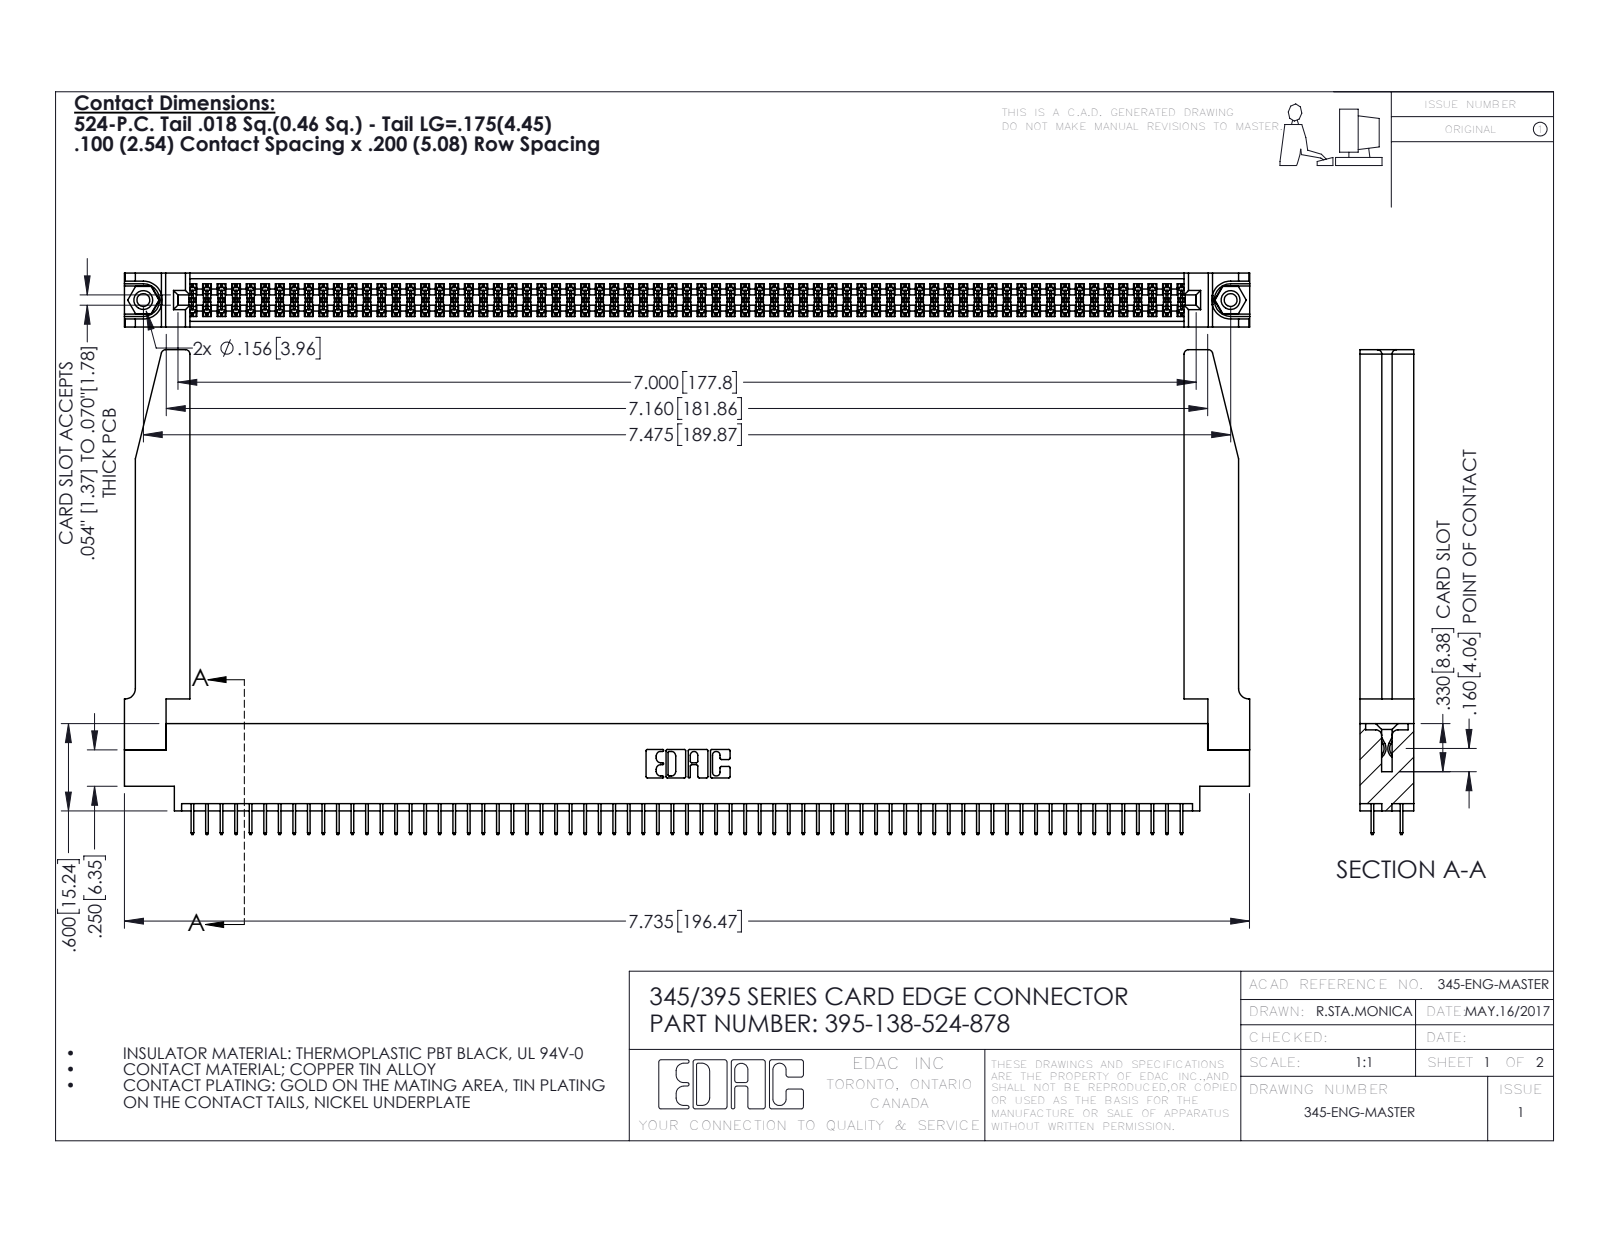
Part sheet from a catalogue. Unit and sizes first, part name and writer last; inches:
Units: inches
Overall size (bounding box): 7.736 × 3.332 × 0.37
Round holes (diameter × count): ⌀0.089 ×2, ⌀0.125 ×2, ⌀0.156 ×2, ⌀0.064 ×1
Round bosses / shafts (diameter × count): ⌀0.155 ×2
Partial cylindrical surfaces — rounded edges, fillets, slot ends (radius × count): R0.006 ×207, R0.01 ×22, R0.03 ×8, R0.007 ×6, R0.031 ×6, R0.026 ×3, R0.014 ×2, R0.019 ×2
Main face-to-face distances: 0.072, 0.37, 0.298, 0.2, 0.098, 0.272, 0.025, 0.225, 0.072, 0.175
Hole centre spacings: 0.27, 7.239, 7.475
Volume: 1.635 in³ · Surface area: 54.35 in²
Bodies: 143 solids, 7816 faces (5608 planar, 2156 cylindrical, 52 other)
Part name (STEP PRODUCT): 345-250-001_345-250-001-102; 345 Part_0.170 Offset - 0.156 Dia-TH; 345-220-078_345-220-078; 395-138-524-878 (+1 more)
STEP written by: SolidWorks 2016 (CONFIG_CONTROL_DESIGN)
